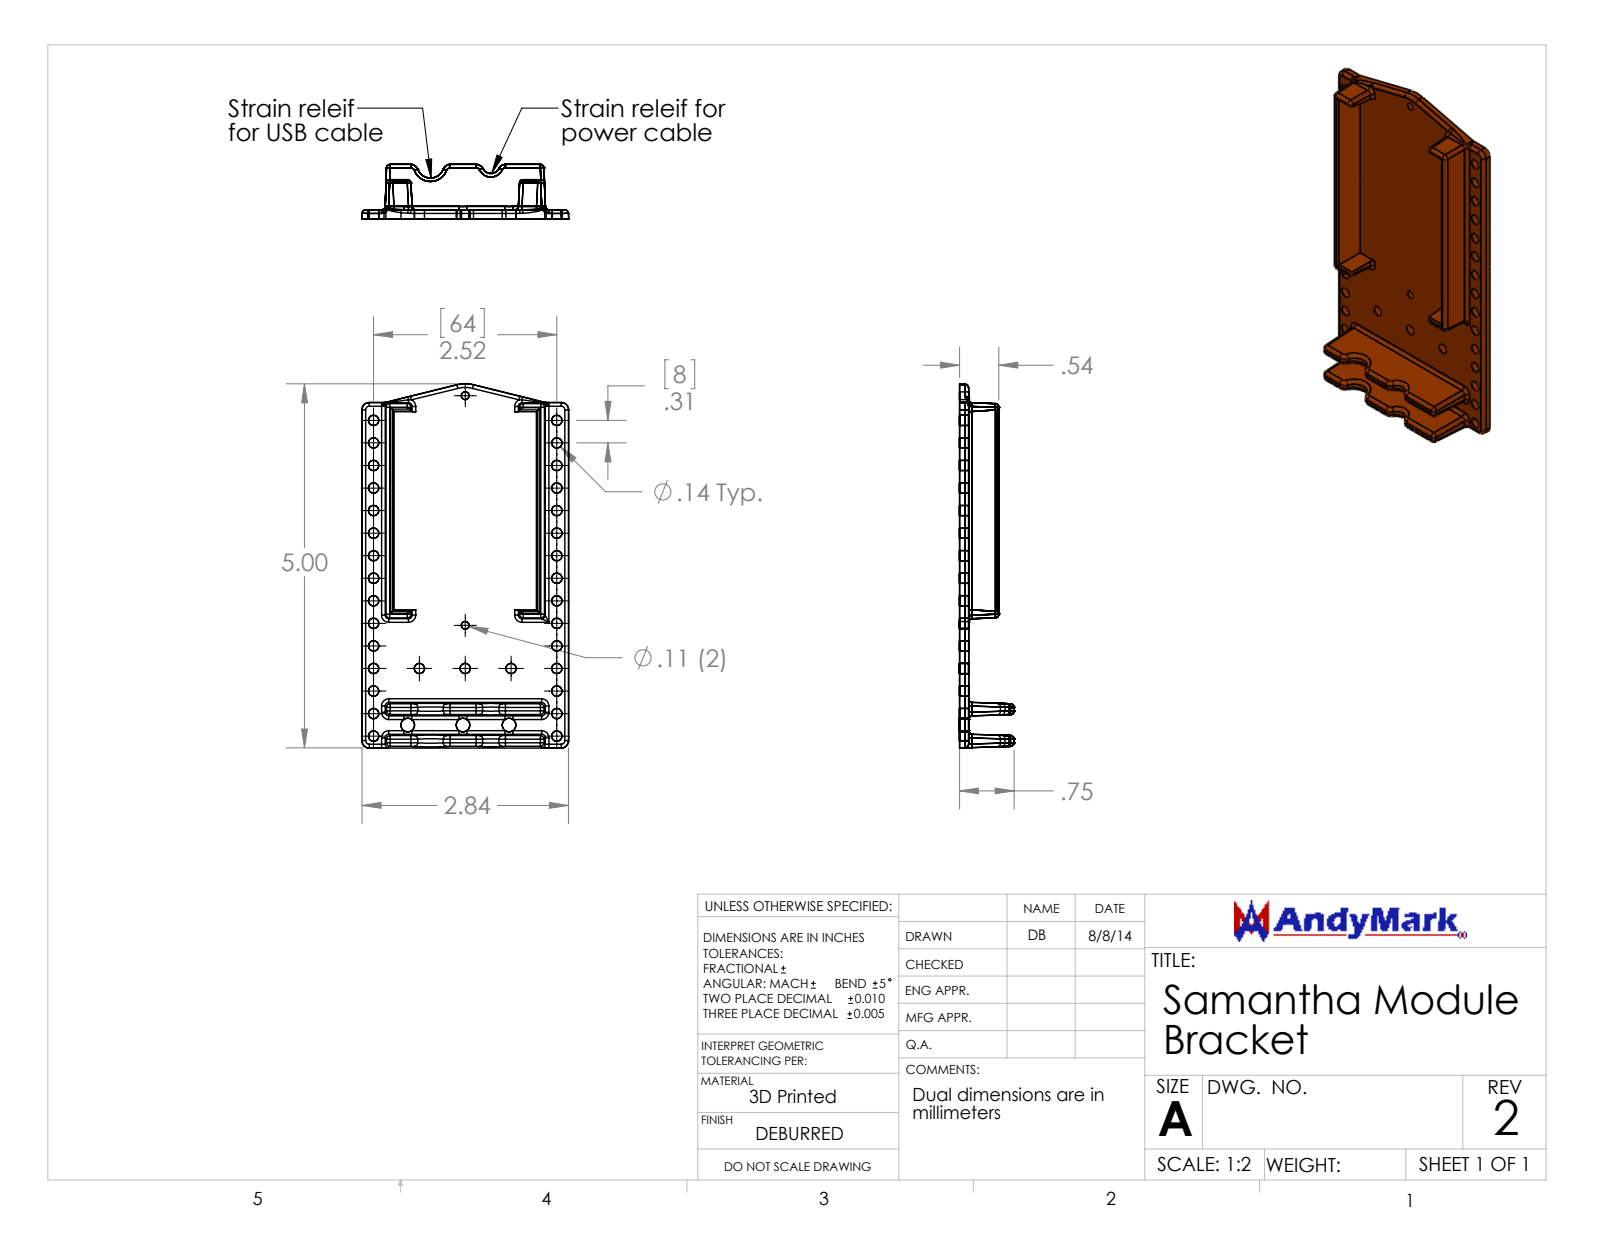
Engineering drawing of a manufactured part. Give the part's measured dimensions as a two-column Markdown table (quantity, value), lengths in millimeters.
| quantity | value |
| --- | --- |
| part name | Samantha Bracket V2 |
| STEP written by | SolidWorks 2014 (AUTOMOTIVE_DESIGN) |
| units | millimeters |
| bodies | 1 solid, 311 faces (48 planar, 167 cylindrical, 96 other) |
| overall size | 127.2 × 72.2 × 19.1 |
| volume | 38 740 mm³ |
| surface area | 25 970 mm² |
| round holes (diameter × count) | 3.6 × 33, 4.7 × 3, 2.7 × 2 |
| partial cylindrical surfaces (radius × count) | 1.3 × 43, 2.5 × 10, 3.2 × 1, 4.7 × 1 |
| main face-to-face distances | 3.2, 11.1, 8, 8, 115.6, 104.5, 45, 33.9, 15.9, 19.1 |
| hole center spacings | 64.5, 65.9, 68.2, 71.3, 15.7, 23.6, 39.4, 75.1 |
